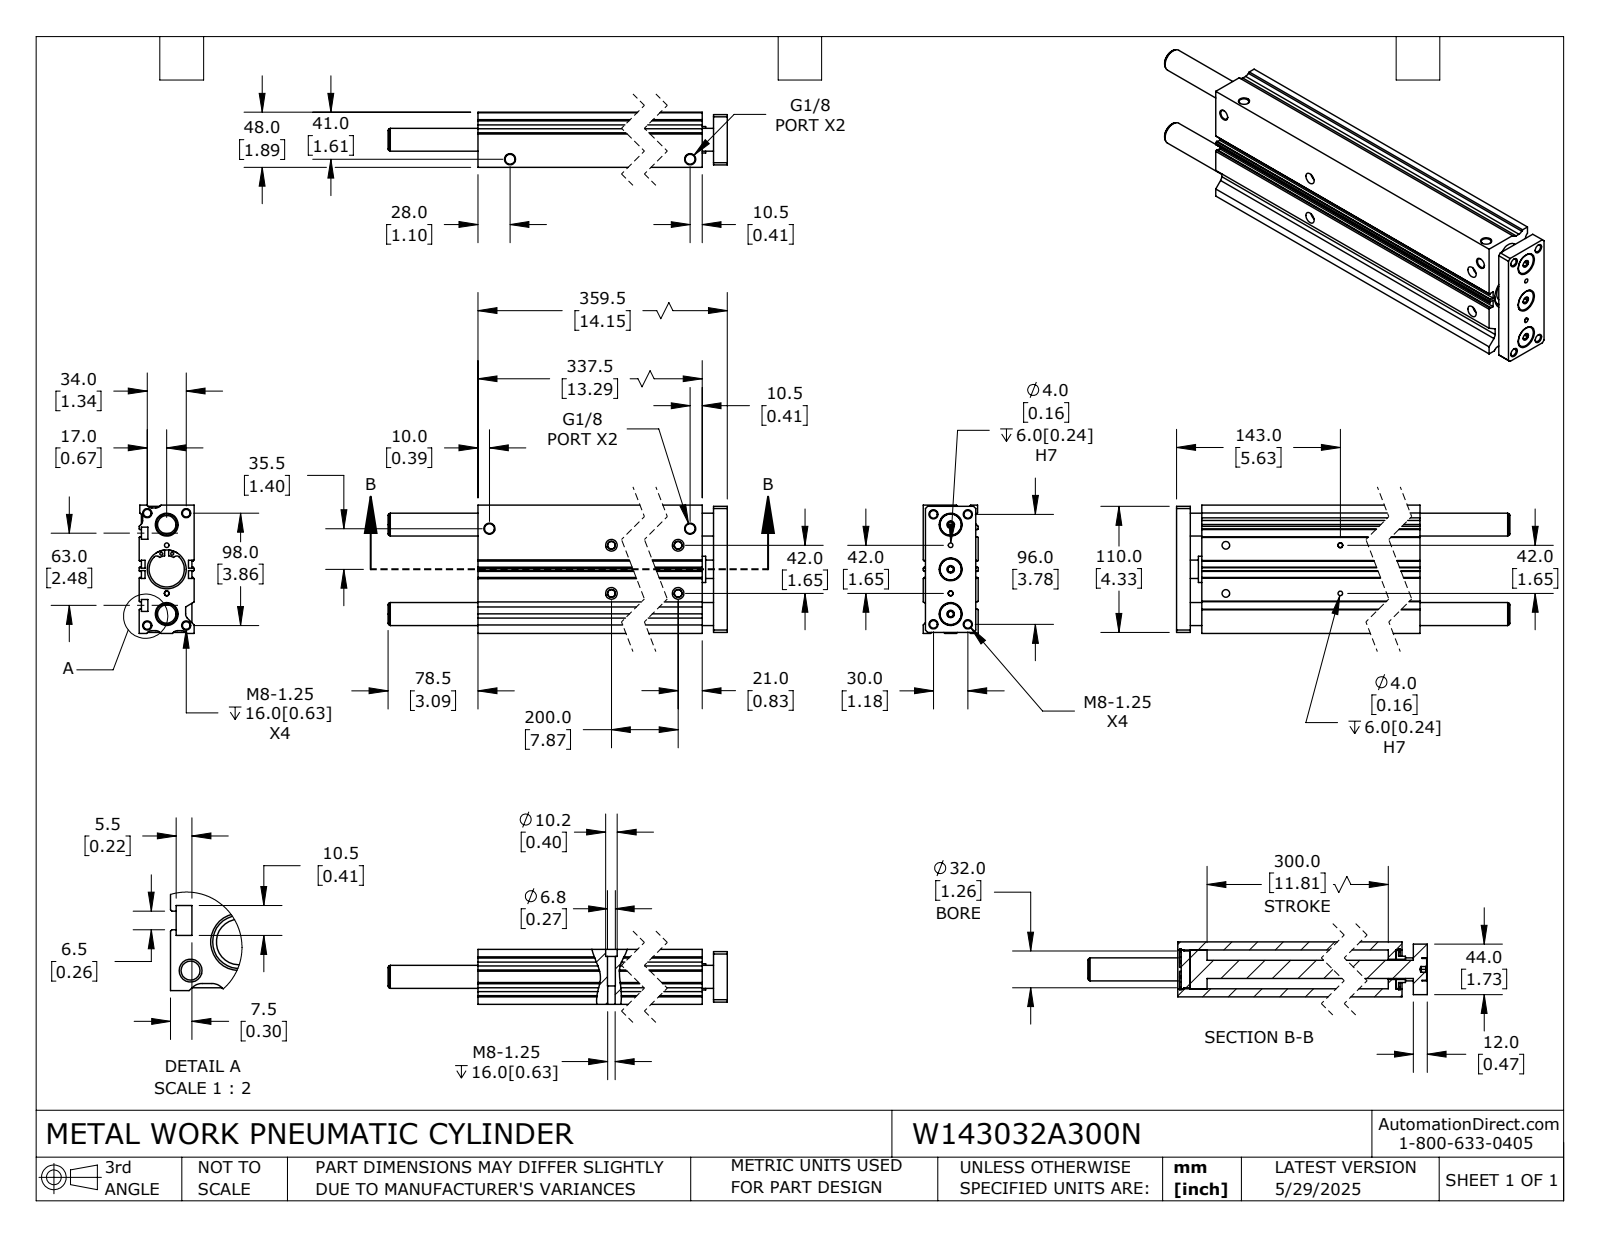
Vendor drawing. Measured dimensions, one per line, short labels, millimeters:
name: W143032A300N_BODY; W143032A300N; W143032A300N_ROD
written by: SolidWorks 2024 (CONFIG_CONTROL_DESIGN)
unit: mm
bodies: 6 solids, 394 faces (195 planar, 149 cylindrical, 50 other)
size: 438 × 112 × 48
volume: 1 537 000 mm³; area: 331 900 mm²
holes: 12× ⌀6.7, 4× ⌀2.5, 4× ⌀4, 4× ⌀6.8, 4× ⌀8.6, 4× ⌀10.2, 3× ⌀5, 3× ⌀20, 1× ⌀17.7, 1× ⌀30.8
bosses: 3× ⌀19, 2× ⌀35.7, 1× ⌀34, 1× ⌀32, 1× ⌀23, 1× ⌀16
rounds: 9× R5, 4× R2, 4× R3, 2× R12.9
face distances: 48, 2.5, 7.5, 43, 5, 40.5, 3, 2, 112, 35.5
hole spacings: 2.2, 8.8, 14.4, 17.5, 19.7, 25.9, 30.9, 32
